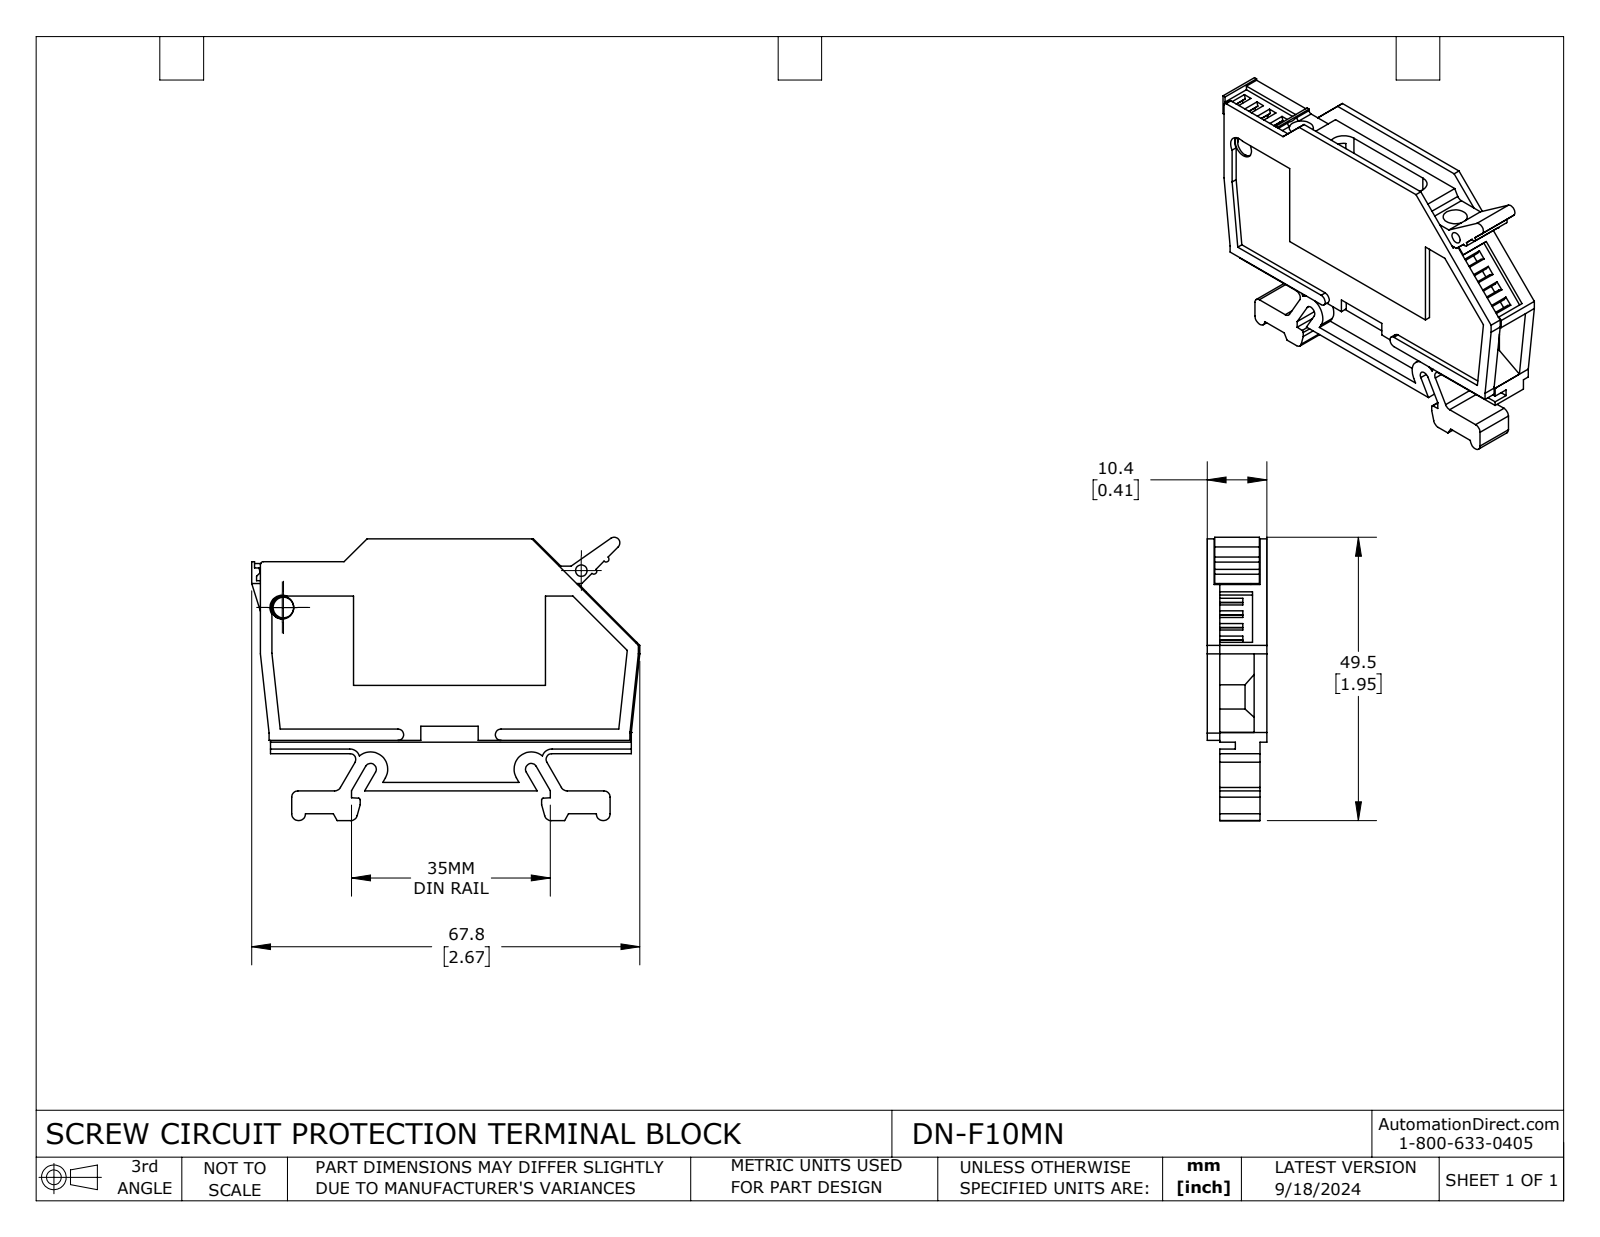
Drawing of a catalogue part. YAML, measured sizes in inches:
part_name: "DN-F10MN"
step_written_by: "SolidWorks 2023 (CONFIG_CONTROL_DESIGN)"
units: inches
bodies: {solids: 1, faces: 440, planar: 292, cylindrical: 78, other: 70}
overall_size: [2.669, 1.948, 0.409]
volume: 0.902
surface_area: 21.57
round_holes:
  - {diameter: 0.165, count: 3}
  - {diameter: 0.079, count: 2}
  - {diameter: 0.098, count: 1}
  - {diameter: 0.157, count: 1}
round_bosses_or_shafts:
  - {diameter: 0.157, count: 1}
partial_cylinders:
  - {radius: 0.039, count: 12}
  - {radius: 0.047, count: 6}
  - {radius: 0.02, count: 4}
  - {radius: 0.049, count: 3}
  - {radius: 0.079, count: 3}
  - {radius: 0.012, count: 2}
  - {radius: 0.043, count: 2}
  - {radius: 0.071, count: 2}
face_to_face_distances: [0.047, 0.039, 0.358, 0.323, 0.362, 0.087, 0.311, 0.079, 0.051, 0.319]
hole_center_spacings: [0.826, 0.828, 1.496, 2.064, 2.072, 2.151]
